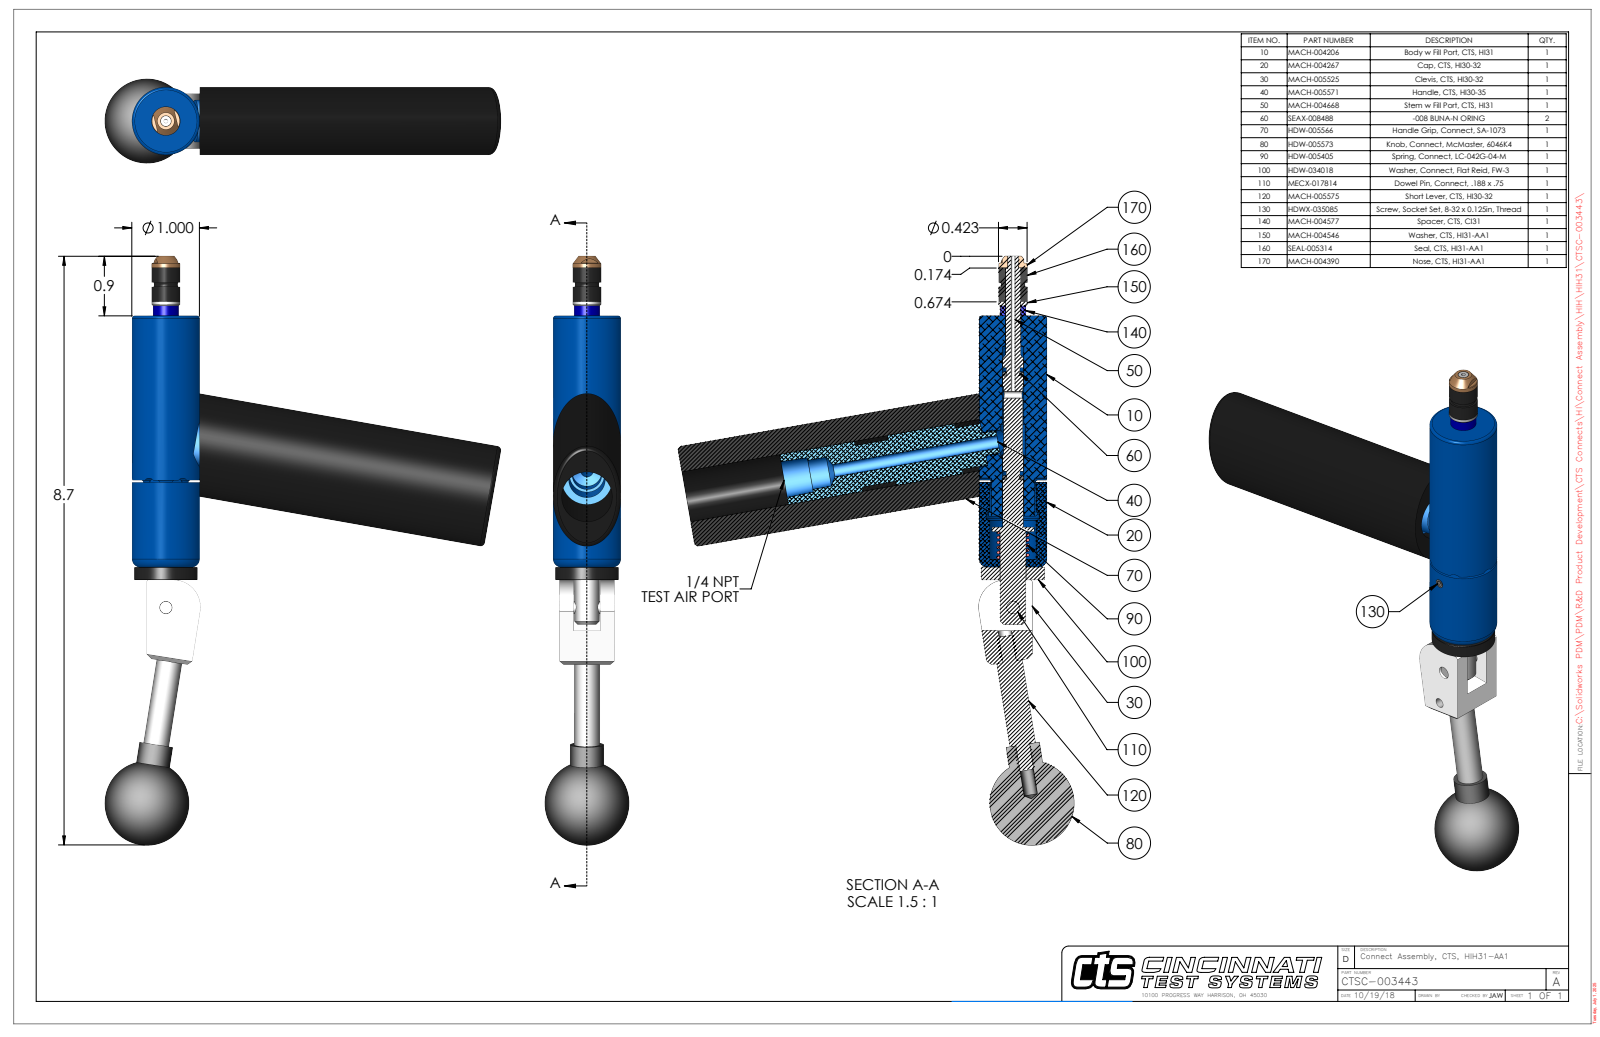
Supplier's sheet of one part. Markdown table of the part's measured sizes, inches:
| quantity | value |
| --- | --- |
| part name | CTSC-003443 |
| STEP written by | SolidWorks 2023 (AUTOMOTIVE_DESIGN) |
| units | inches |
| bodies | 11 solids, 294 faces (102 planar, 124 cylindrical, 68 other) |
| overall size | 8.704 × 5.856 × 1.25 |
| volume | 9.166 in³ |
| surface area | 74.32 in² |
| round holes (diameter × count) | 0.201 × 2, 0.063 × 1, 0.104 × 1, 0.109 × 1, 0.136 × 1, 0.15 × 1, 0.159 × 1, 0.187 × 1, 0.189 × 1, 0.218 × 1, 0.228 × 1, 0.229 × 1 |
| round bosses / shafts (diameter × count) | 1 × 1, 0.936 × 1, 0.75 × 1, 0.62 × 1, 0.5 × 1, 0.423 × 1, 0.38 × 1, 0.379 × 1 |
| partial cylindrical surfaces (radius × count) | 0.093 × 6, 0.029 × 2, 0.325 × 1, 0.4 × 1, 0.463 × 1 |
| main face-to-face distances | 0.21, 0.602, 0.812, 0.187, 3.713, 3.901, 0.785, 0.391, 2.46, 1.253 |
| hole center spacings | 0.599, 1.658, 2.252 |
